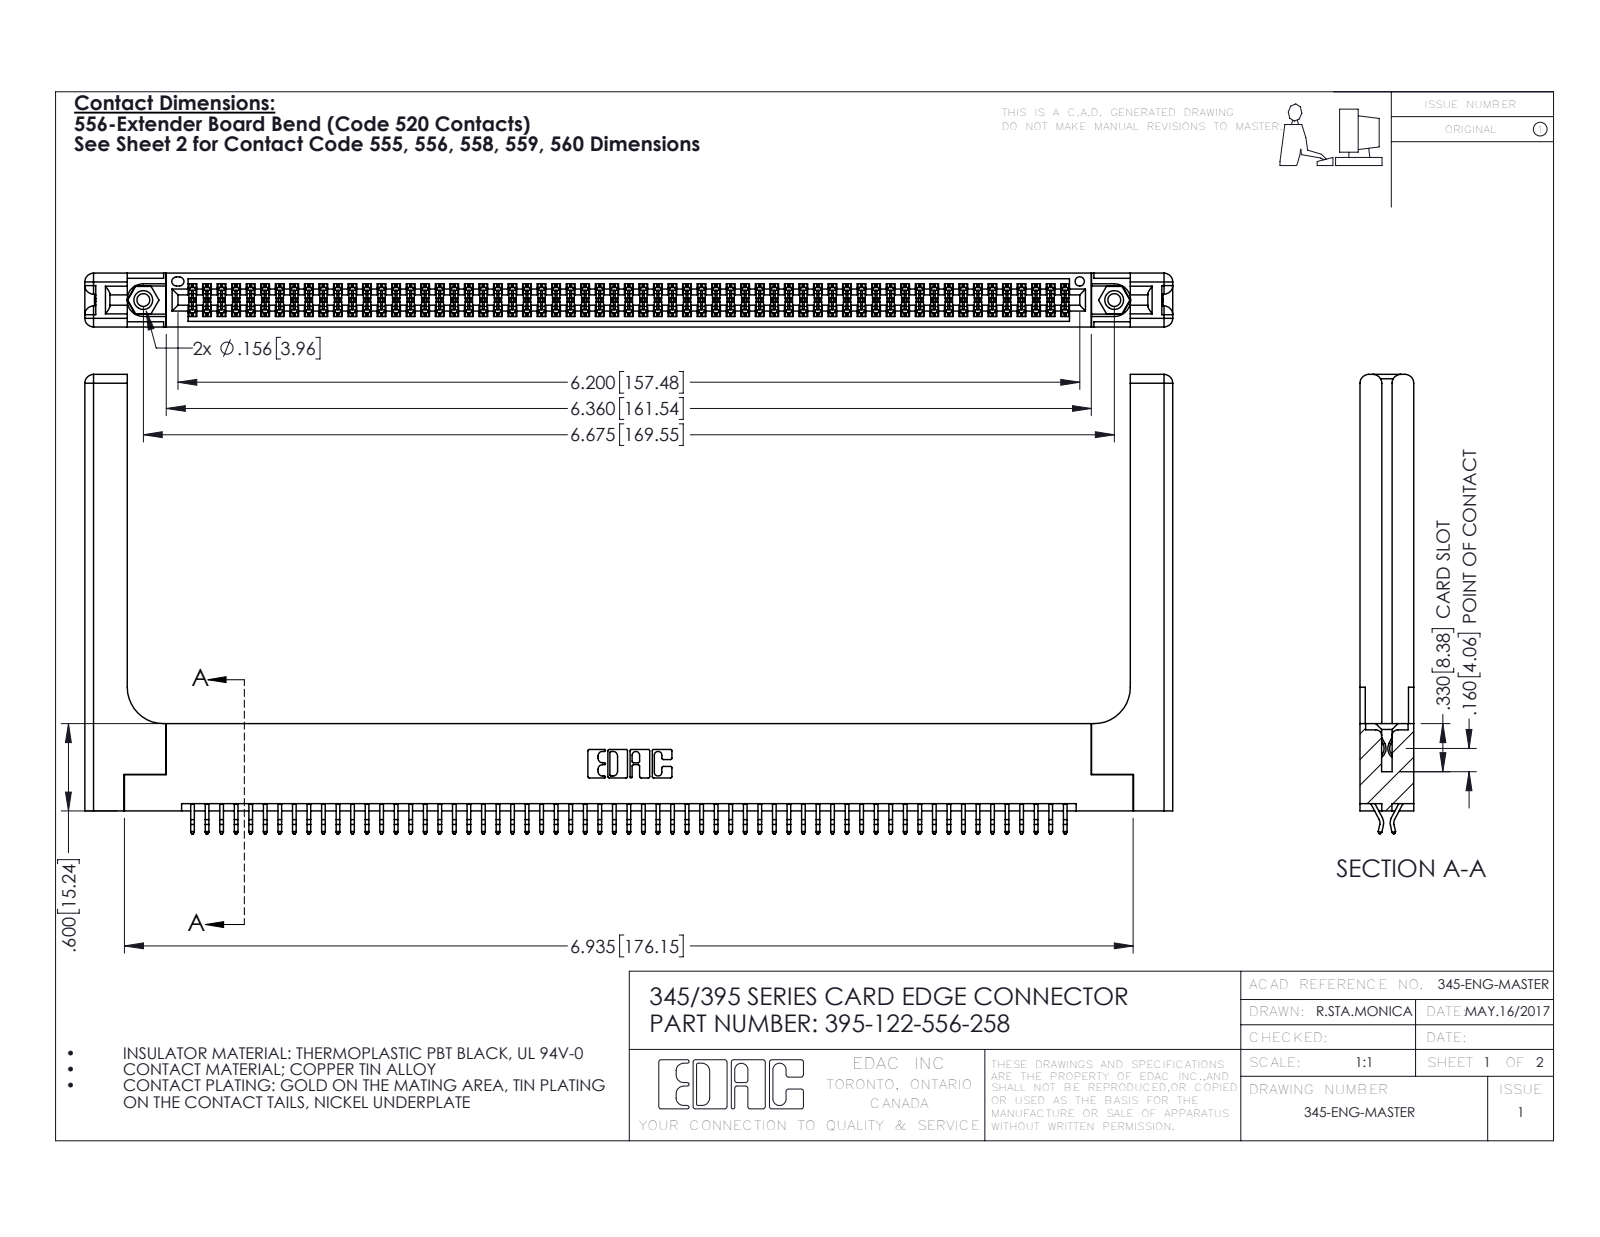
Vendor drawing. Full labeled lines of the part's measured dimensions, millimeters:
Part name (STEP PRODUCT): 345-250-001_345-250-001-102; 345-292-001_556 Tail; 345 Part_Flush Mounting Lugs - 0.156 Dia-TH; 345-220-058_345-220-058 (+1 more)
STEP written by: SolidWorks 2016 (CONFIG_CONTROL_DESIGN)
Units: millimetres
Bodies: 127 solids, 7214 faces (4742 planar, 2412 cylindrical, 60 other)
Overall size (bounding box): 190 × 80.2 × 9.4
Volume: 27 100 mm³ · Surface area: 32 850 mm²
Round holes (diameter × count): ⌀2.3 ×2, ⌀3.2 ×2, ⌀4 ×2, ⌀1.6 ×1
Round bosses / shafts (diameter × count): ⌀3.9 ×2
Partial cylindrical surfaces — rounded edges, fillets, slot ends (radius × count): R0.2 ×183, R0.3 ×22, R1.5 ×16, R0.2 ×6, R0.8 ×6, R0.7 ×3, R0.3 ×2, R0.4 ×2
Main face-to-face distances: 1.8, 7.6, 9.4, 5.1, 0.6, 2.5, 6.9, 5.7, 3.8, 3.8
Hole centre spacings: 6.9, 163.6, 169.5
